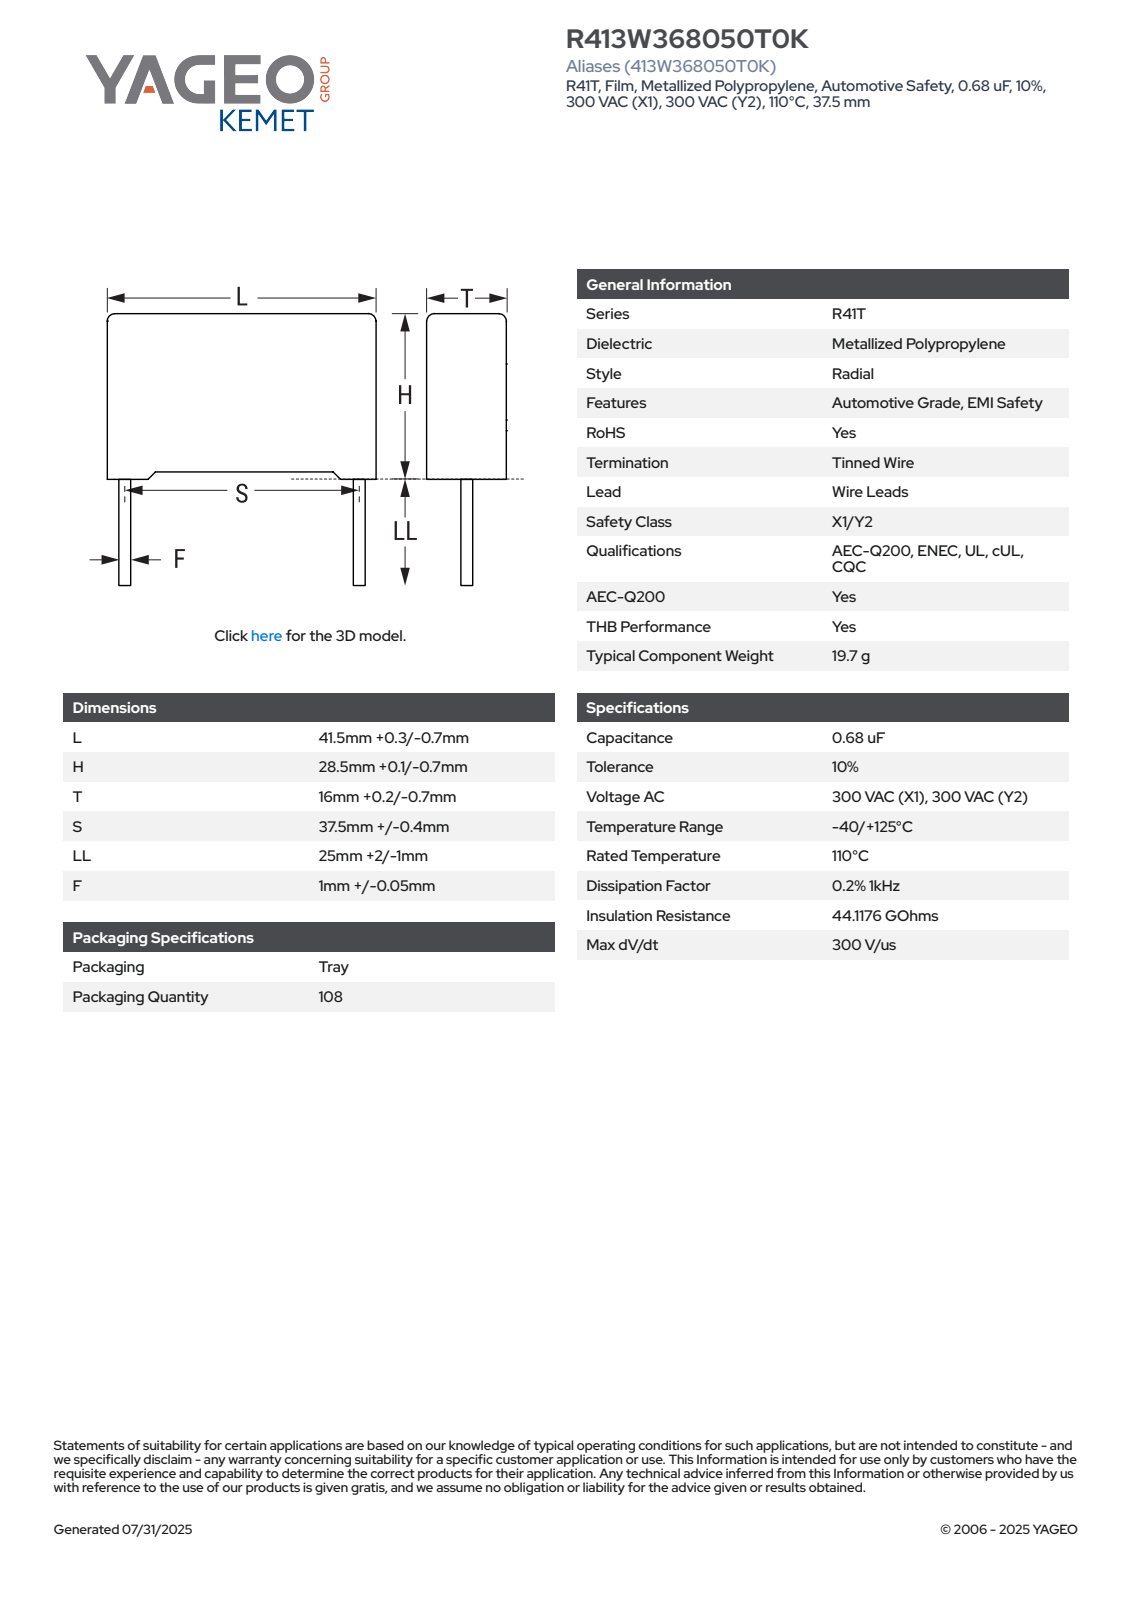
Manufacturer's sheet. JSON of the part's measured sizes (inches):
{"part_name": "CFR_RB2_41.5X28.5X16_L41.8H28.6T16.2S37.5LL27F1.05", "step_written_by": "SolidWorks 2021 (AUTOMOTIVE_DESIGN)", "units": "inches", "bodies": {"solids": 4, "faces": 85, "planar": 77, "cylindrical": 8, "other": 0}, "overall_size": [2.189, 1.646, 0.638], "volume_in3": 1.149, "surface_area_in2": 7.638, "round_bosses_or_shafts": [[0.041, 2]], "partial_cylinders_radius": [[0.02, 4]], "face_to_face_distances": [0.638, 1.087, 1.646, 1.096, 0.03, 0.039, 1.126, 0.638, 0.055, 1.591]}
